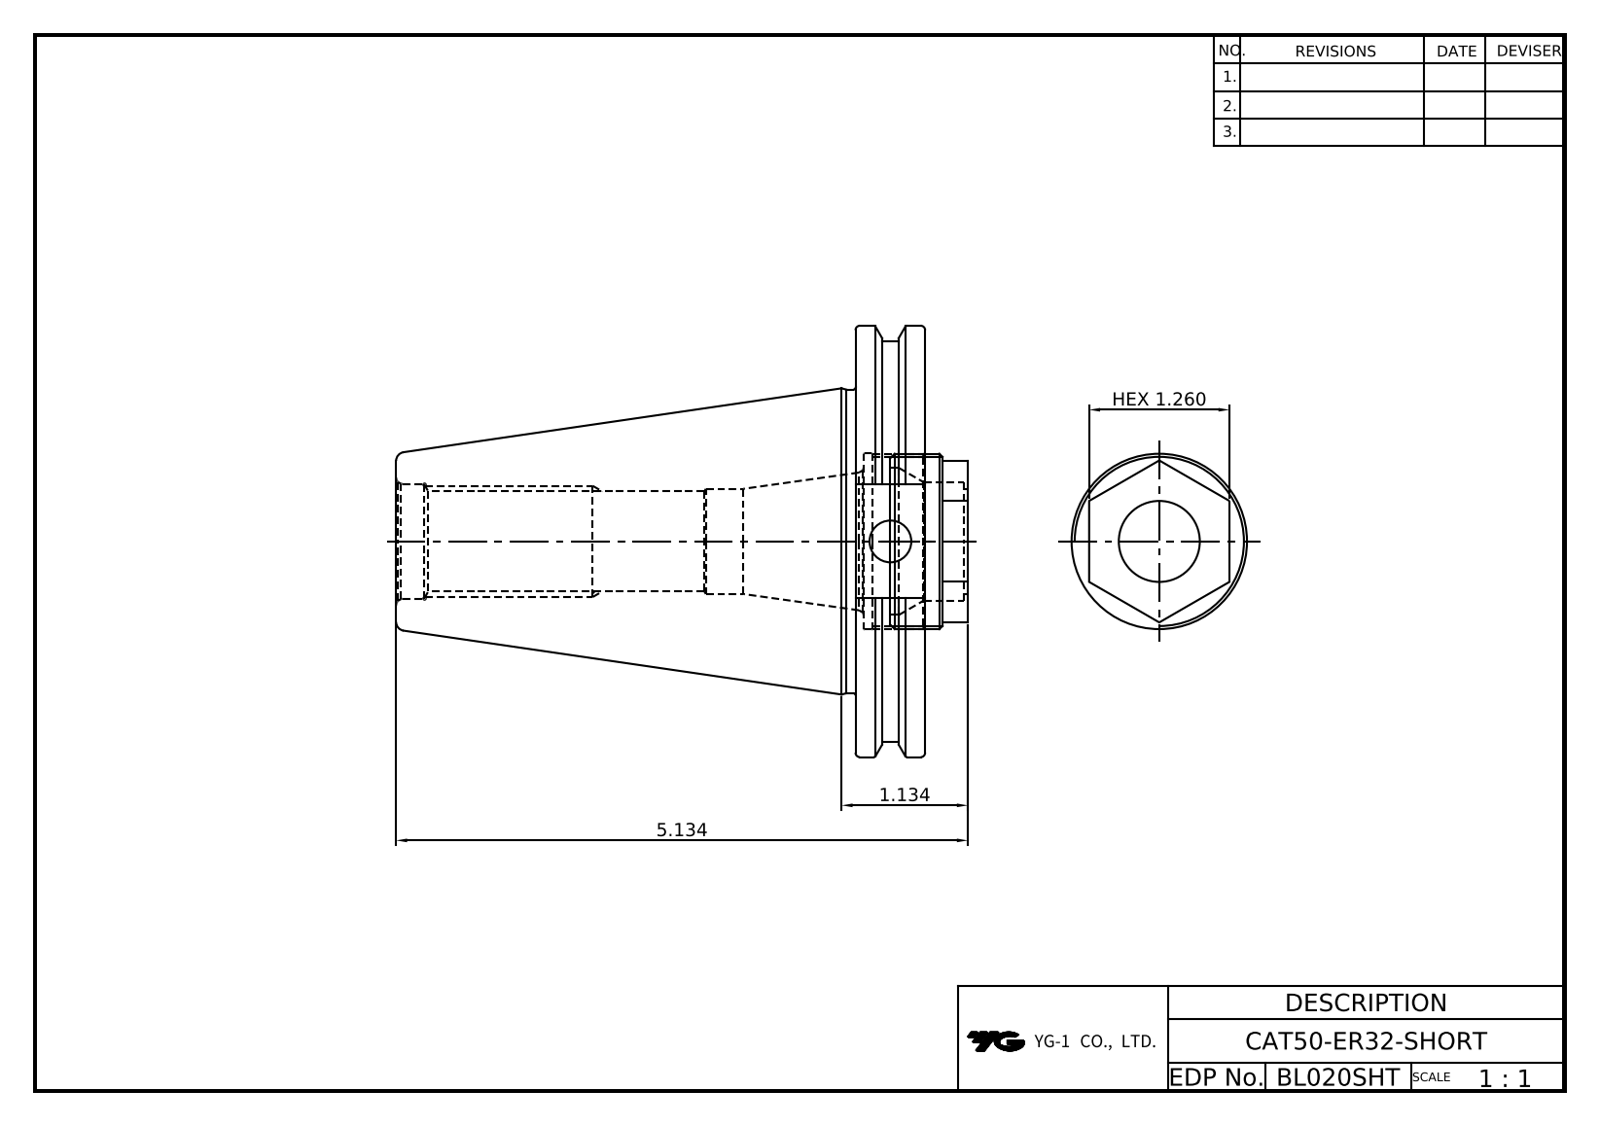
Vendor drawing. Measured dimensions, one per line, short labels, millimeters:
name: LO-CAT50-ER32-SHORT; ER32(SHORT TYPE)
written by: Autodesk Inventor 2025 (AUTOMOTIVE_DESIGN)
unit: mm
bodies: 2 solids, 75 faces (39 planar, 16 cylindrical, 20 other)
size: 124.45 × 98.42 × 94.69
volume: 309 245 mm³; area: 49 851 mm²
holes: 1× ⌀9.53, 1× ⌀21.97, 1× ⌀24, 1× ⌀26.2, 1× ⌀27, 1× ⌀38.38, 1× ⌀40.2
bosses: 1× ⌀98.42, 1× ⌀91.29, 1× ⌀69.25, 1× ⌀40
face distances: 15.88, 1.88, 14, 104.77, 106.65, 120.65, 124.45, 19.68, 17.8, 3.8
